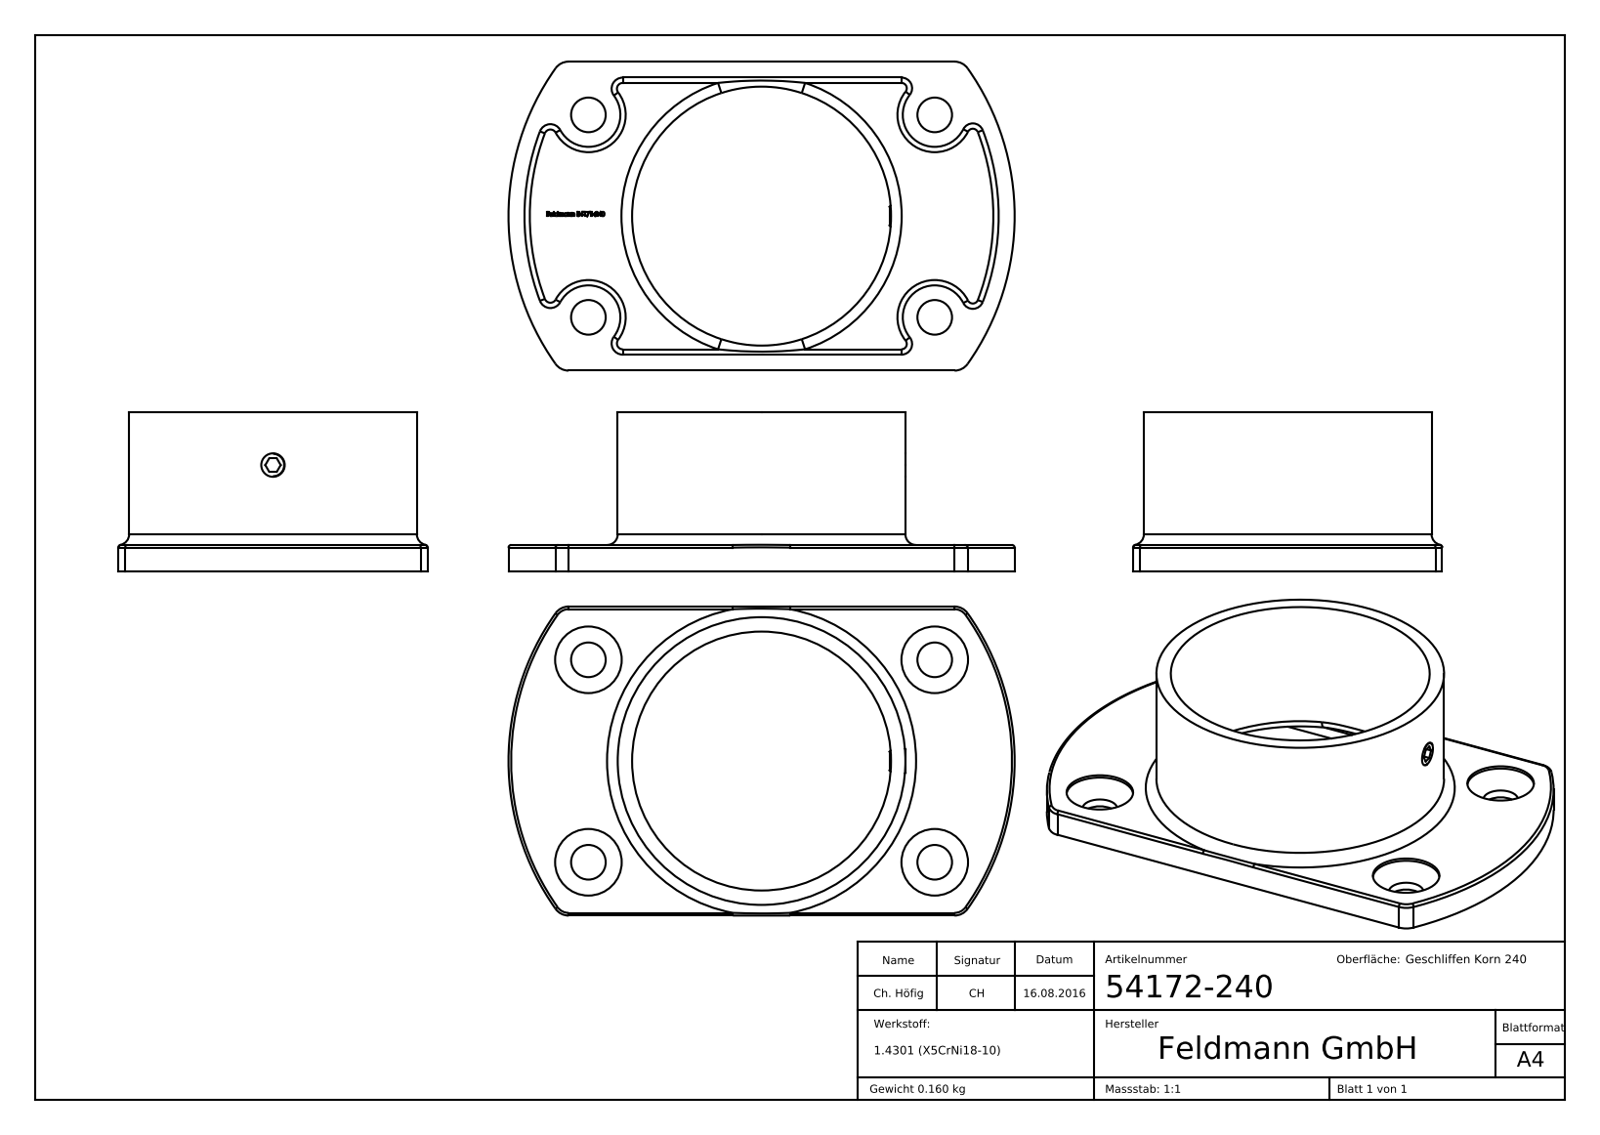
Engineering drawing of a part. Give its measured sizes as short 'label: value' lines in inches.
name: DIN913 M5x3; 54172-240; 54172-240 Teil1; DIN913 M5x3_DIN913 M5x6
written by: SolidWorks 2018 (CONFIG_CONTROL_DESIGN)
unit: in
bodies: 2 solids, 298 faces (156 planar, 38 cylindrical, 104 other)
size: 3.74 × 2.283 × 1.181
volume: 1.236 in³; area: 26.24 in²
holes: 4× ⌀0.256, 4× ⌀0.492, 1× ⌀0.165, 1× ⌀1.913
bosses: 1× ⌀2.126, 1× ⌀0.197
rounds: 4× R0.079, 4× R0.083, 4× R0.118, 4× R0.236, 2× R0.02, 2× R0.039, 2× R1.772, 2× R1.89
face distances: 0.118, 0.079, 0.197, 1.181, 1.063, 0.984, 2.283, 2.165, 2.047, 0.098
hole spacings: 1.482, 1.496, 2.559, 2.964
